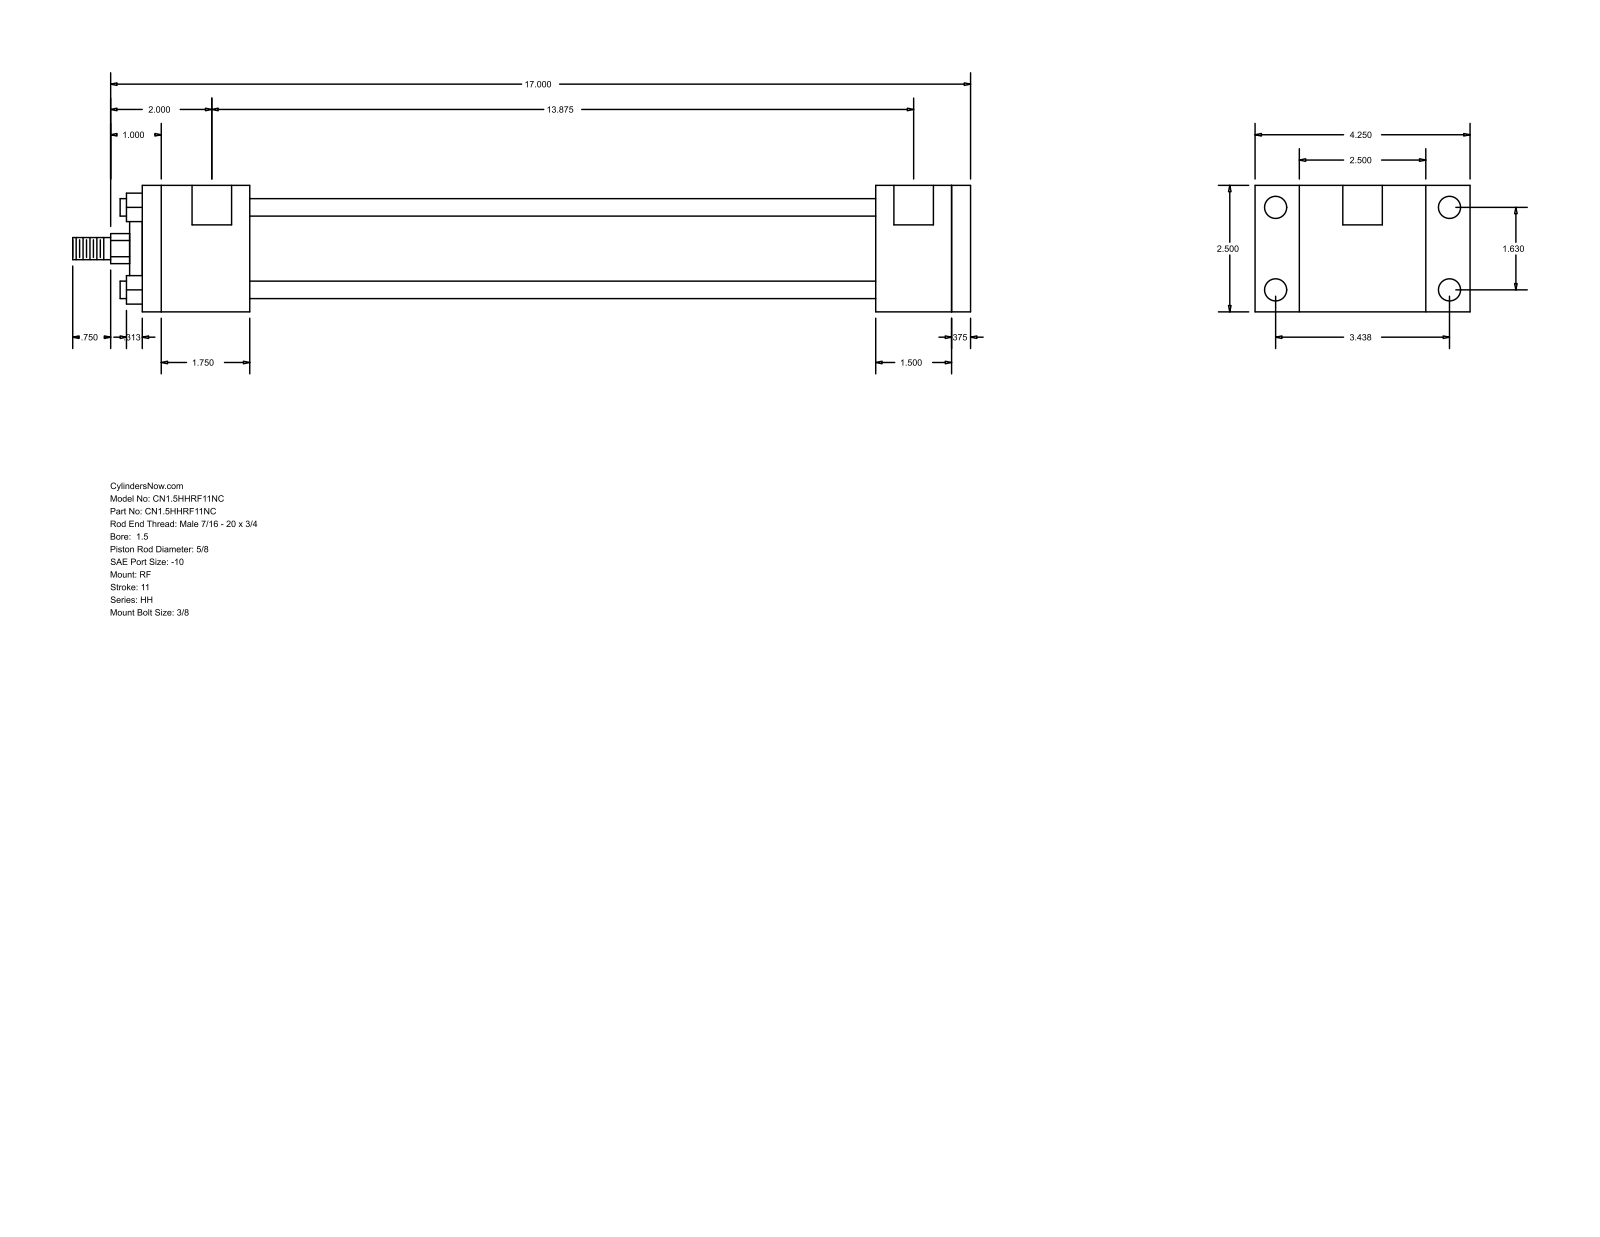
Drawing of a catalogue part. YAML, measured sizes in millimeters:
part_name: "HH_RF__0150_0.625"
step_written_by: "GSSL Pune (CONFIG_CONTROL_DESIGN)"
units: millimeters
bodies: {solids: 0, faces: 92, planar: 64, cylindrical: 28, other: 0}
overall_size: [450.85, 107.95, 63.5]
round_holes:
  - {diameter: 5.56, count: 4}
  - {diameter: 11.13, count: 4}
  - {diameter: 19.84, count: 2}
round_bosses_or_shafts:
  - {diameter: 8.76, count: 4}
  - {diameter: 44.45, count: 1}
  - {diameter: 28.57, count: 1}
  - {diameter: 15.88, count: 1}
  - {diameter: 11.11, count: 1}
partial_cylinders:
  - {radius: 7.54, count: 1}
face_to_face_distances: [63.5, 415.92, 9.53, 406.39, 53.97, 368.3, 314.33, 352.42, 361.95, 38.09]
hole_center_spacings: [41.4, 87.32, 96.64, 355.6, 1.58, 1.59, 352.43, 354.01]
